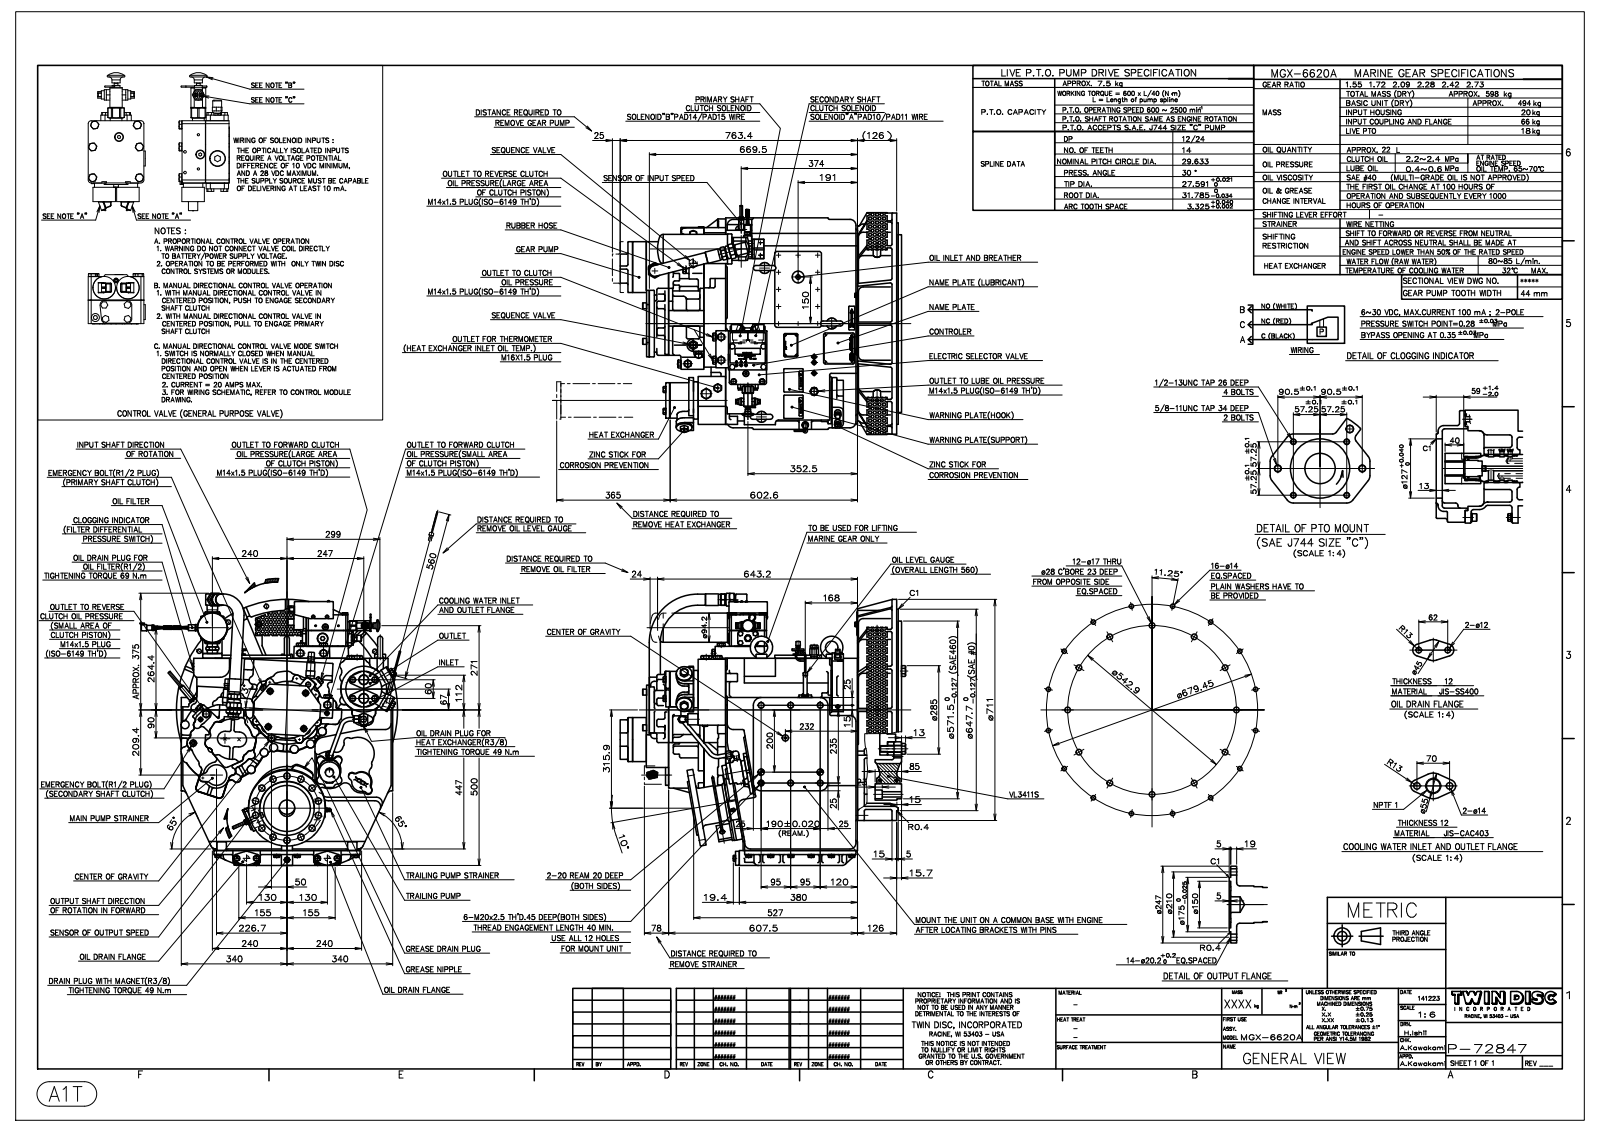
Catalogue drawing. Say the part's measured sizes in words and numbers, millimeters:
The part is named "P72847". Its 3-D file was written by "SolidWorks 2010 (AUTOMOTIVE_DESIGN)". It is 0 solids with 4438 faces: 1595 planar, 1830 cylindrical and 1013 other. Overall it measures 917.7 by 859.49 by 747.93 millimeters. Round holes: 40 of diameter 10, 16 of diameter 14, 14 of diameter 20.3, 12 of diameter 15, 12 of diameter 17, 8 of diameter 20, 7 of diameter 8, 6 of diameter 30.5, 4 of diameter 12.7, 3 of diameter 19, 3 of diameter 30, 2 of diameter 45.5. Round bosses or shafts: 12 of diameter 12, 7 of diameter 35, 7 of diameter 26, 5 of diameter 22, 4 of diameter 15.7, 3 of diameter 50, 3 of diameter 38, 3 of diameter 32. Partial cylindrical surfaces (rounded edges, fillets, slot ends): 211 of radius 10, 99 of radius 12, 66 of radius 13, 46 of radius 3, 43 of radius 5, 31 of radius 19, 28 of radius 14, 24 of radius 50. The main face-to-face distances are 5, 424, 618, 10, 141.7, 70, 494, 13, 15, 61.7. The hole center spacings are 46.73, 130.93, 189.2, 480.44, 627.73, 132.55, 204.74, 377.48.
